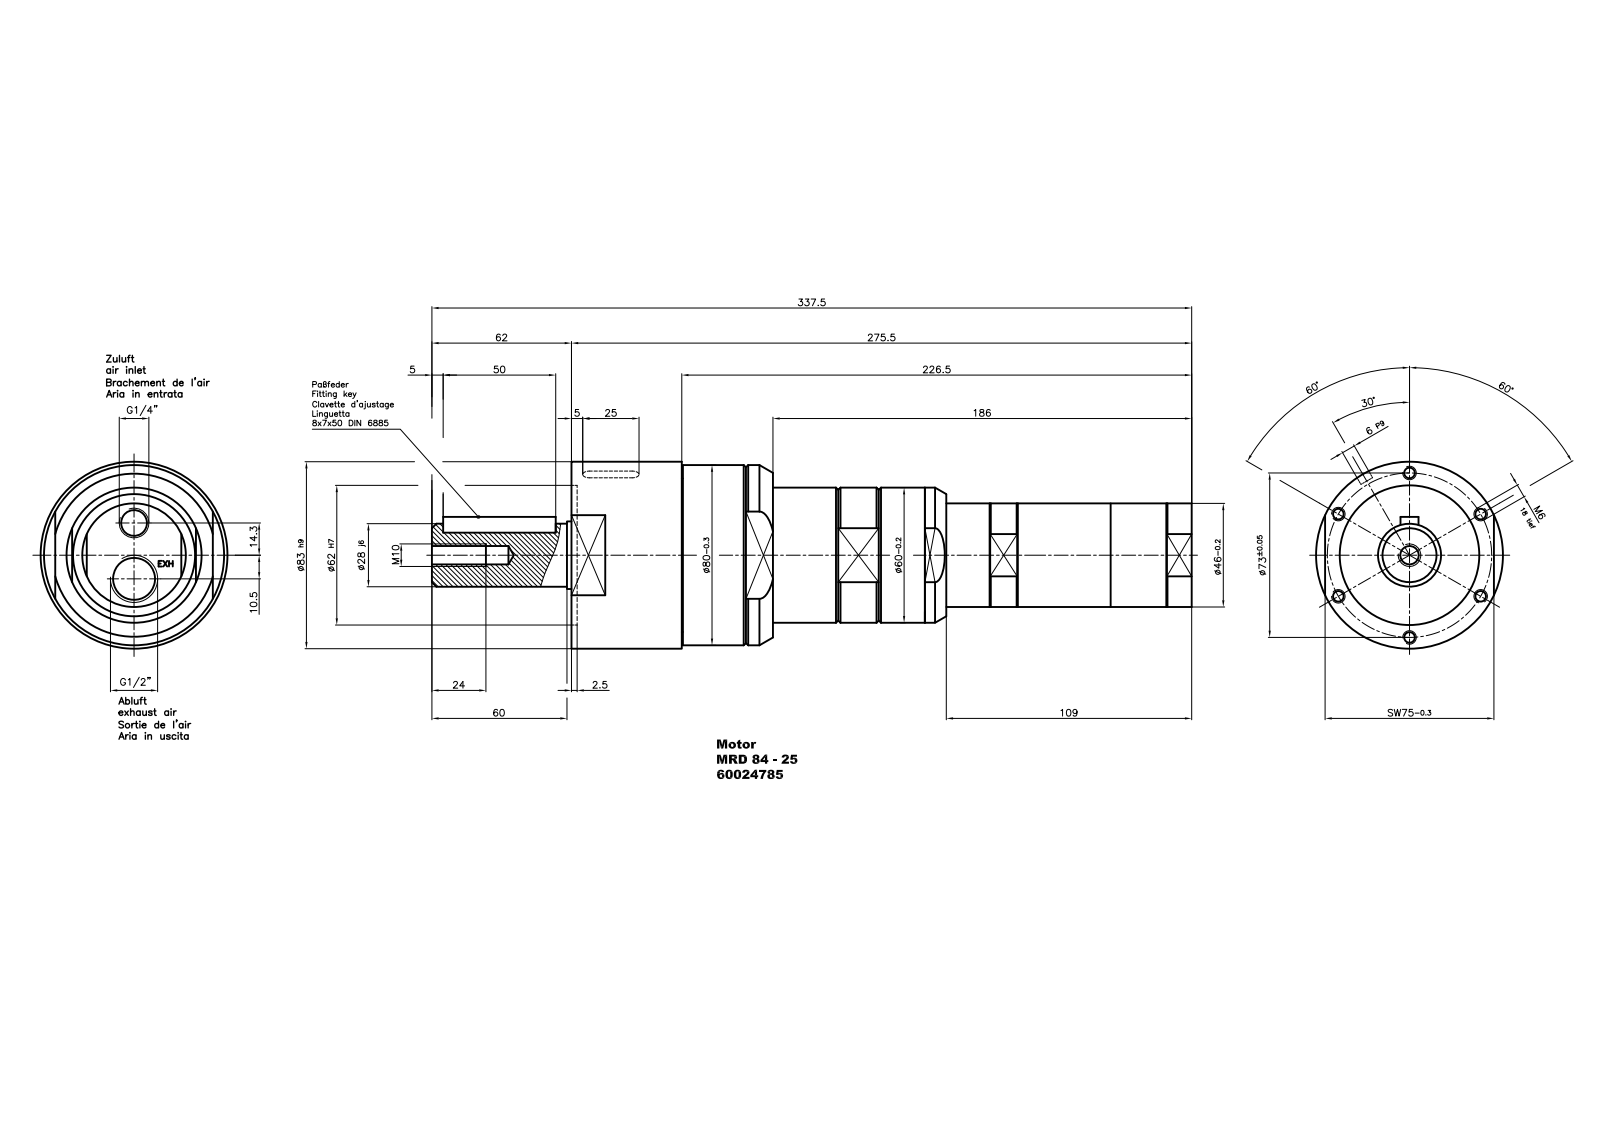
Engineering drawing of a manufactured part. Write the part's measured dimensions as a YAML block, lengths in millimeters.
part_name: "MRD 84-337; 9314731 Sicherungsring"
step_written_by: "Autodesk Inventor 2012 (AUTOMOTIVE_DESIGN)"
units: millimeters
bodies: {solids: 3, faces: 190, planar: 100, cylindrical: 52, other: 38}
overall_size: [337.5, 83, 83]
volume: 873682
surface_area: 85968
round_holes:
  - {diameter: 4.92, count: 5}
  - {diameter: 1.55, count: 2}
  - {diameter: 2.5, count: 2}
  - {diameter: 5.5, count: 2}
  - {diameter: 4.92, count: 1}
  - {diameter: 8.38, count: 1}
  - {diameter: 11.45, count: 1}
  - {diameter: 18.63, count: 1}
  - {diameter: 38, count: 1}
  - {diameter: 46.5, count: 1}
  - {diameter: 58.69, count: 1}
  - {diameter: 62, count: 1}
round_bosses_or_shafts:
  - {diameter: 5, count: 2}
  - {diameter: 83, count: 1}
  - {diameter: 80, count: 1}
  - {diameter: 68.16, count: 1}
  - {diameter: 60, count: 1}
  - {diameter: 46, count: 1}
  - {diameter: 45, count: 1}
  - {diameter: 30, count: 1}
partial_cylinders:
  - {radius: 2.25, count: 2}
  - {radius: 3, count: 2}
  - {radius: 4, count: 2}
face_to_face_distances: [5, 49, 0.5, 44, 157, 152, 108, 107.5, 46.5, 49.5]
hole_center_spacings: [36.5, 63.22, 73, 26.98, 28.45, 31.86, 32.55, 42.73]
